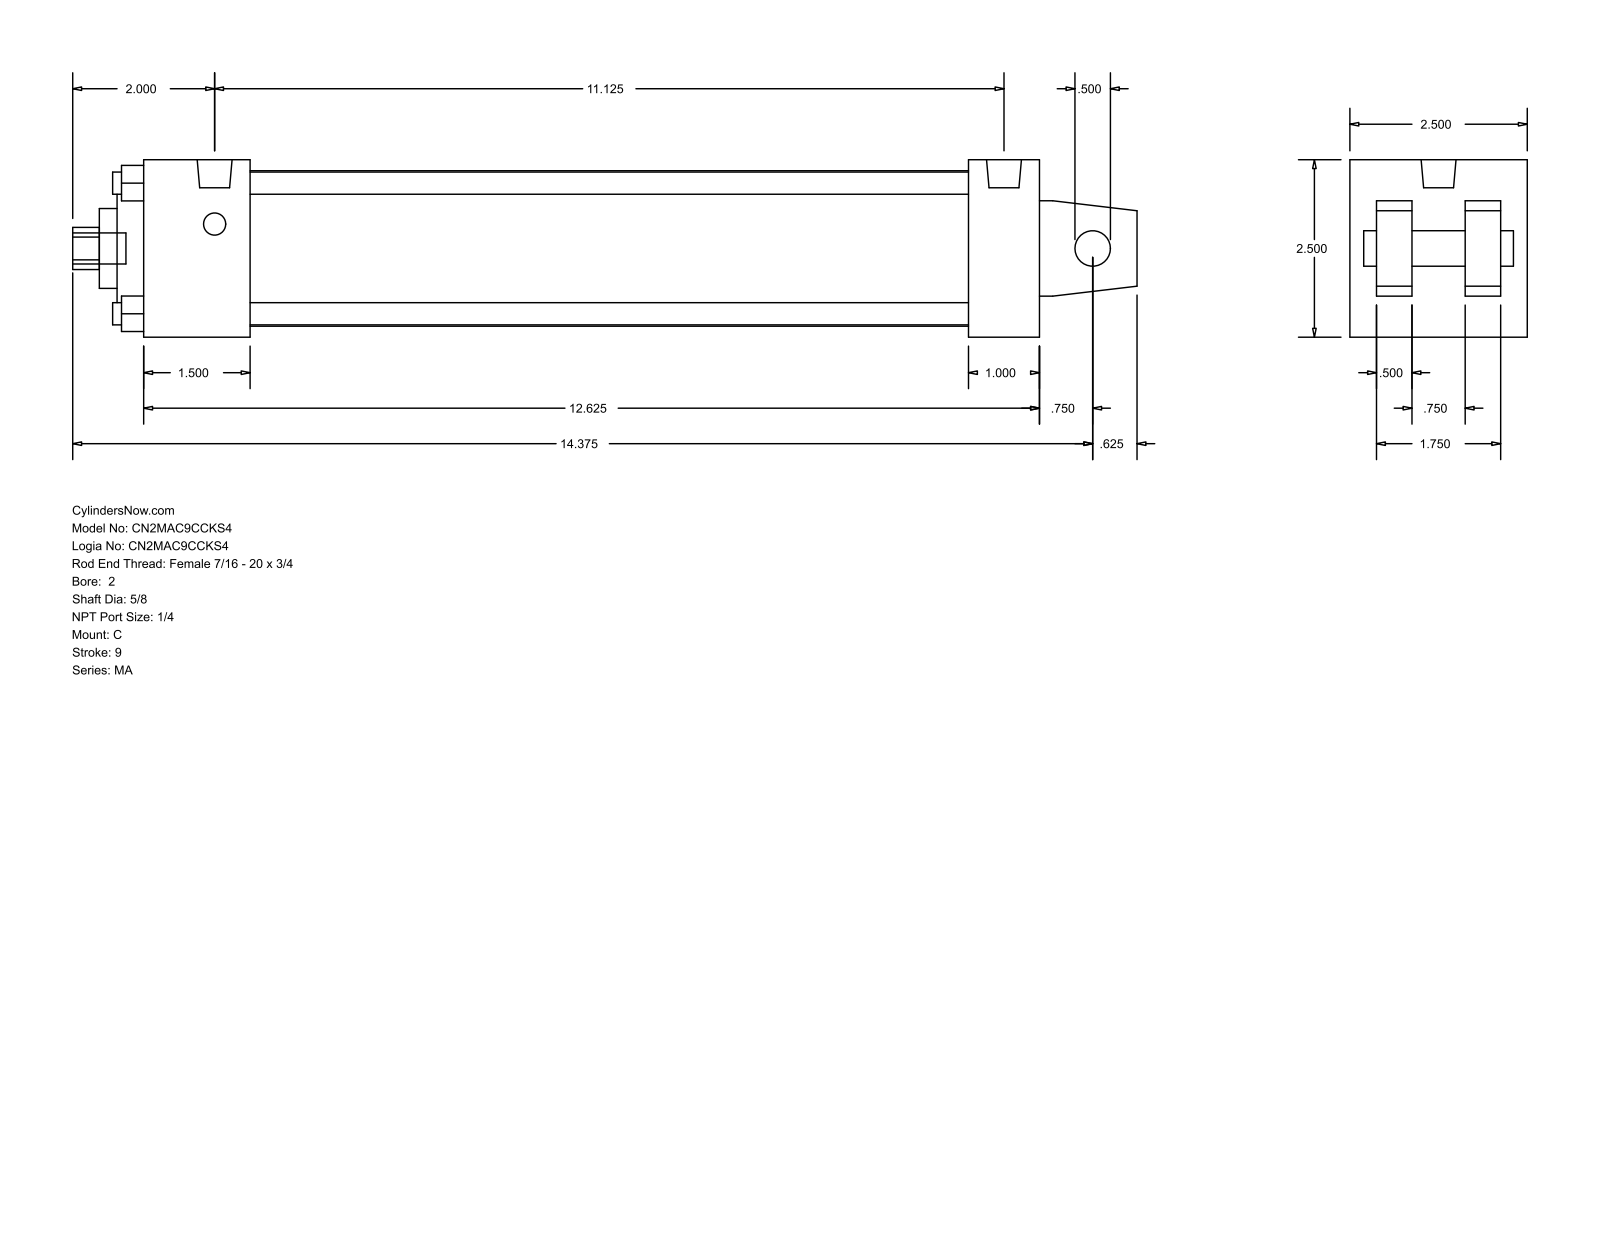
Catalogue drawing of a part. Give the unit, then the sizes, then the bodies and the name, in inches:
Units: inches
Overall size (bounding box): 15 × 2.5 × 2.5
Round holes (diameter × count): ⌀0.313 ×4, ⌀0.5 ×1, ⌀0.625 ×1, ⌀1.125 ×1, ⌀2 ×1, ⌀2.19 ×1
Round bosses / shafts (diameter × count): ⌀0.313 ×4, ⌀0.492 ×2, ⌀0.437 ×1
Partial cylindrical surfaces — rounded edges, fillets, slot ends (radius × count): R0.297 ×1
Main face-to-face distances: 2.5, 0.375, 0.5, 0.875, 1.625, 2.125, 1.25, 1.5, 12.625, 11.125
Hole centre spacings: 1.301, 1.84, 2.602
Bodies: 0 solids, 105 faces (77 planar, 28 cylindrical, 0 other)
Part name (STEP PRODUCT): MA_C__0200_0.625
STEP written by: GSSL Pune (CONFIG_CONTROL_DESIGN)
